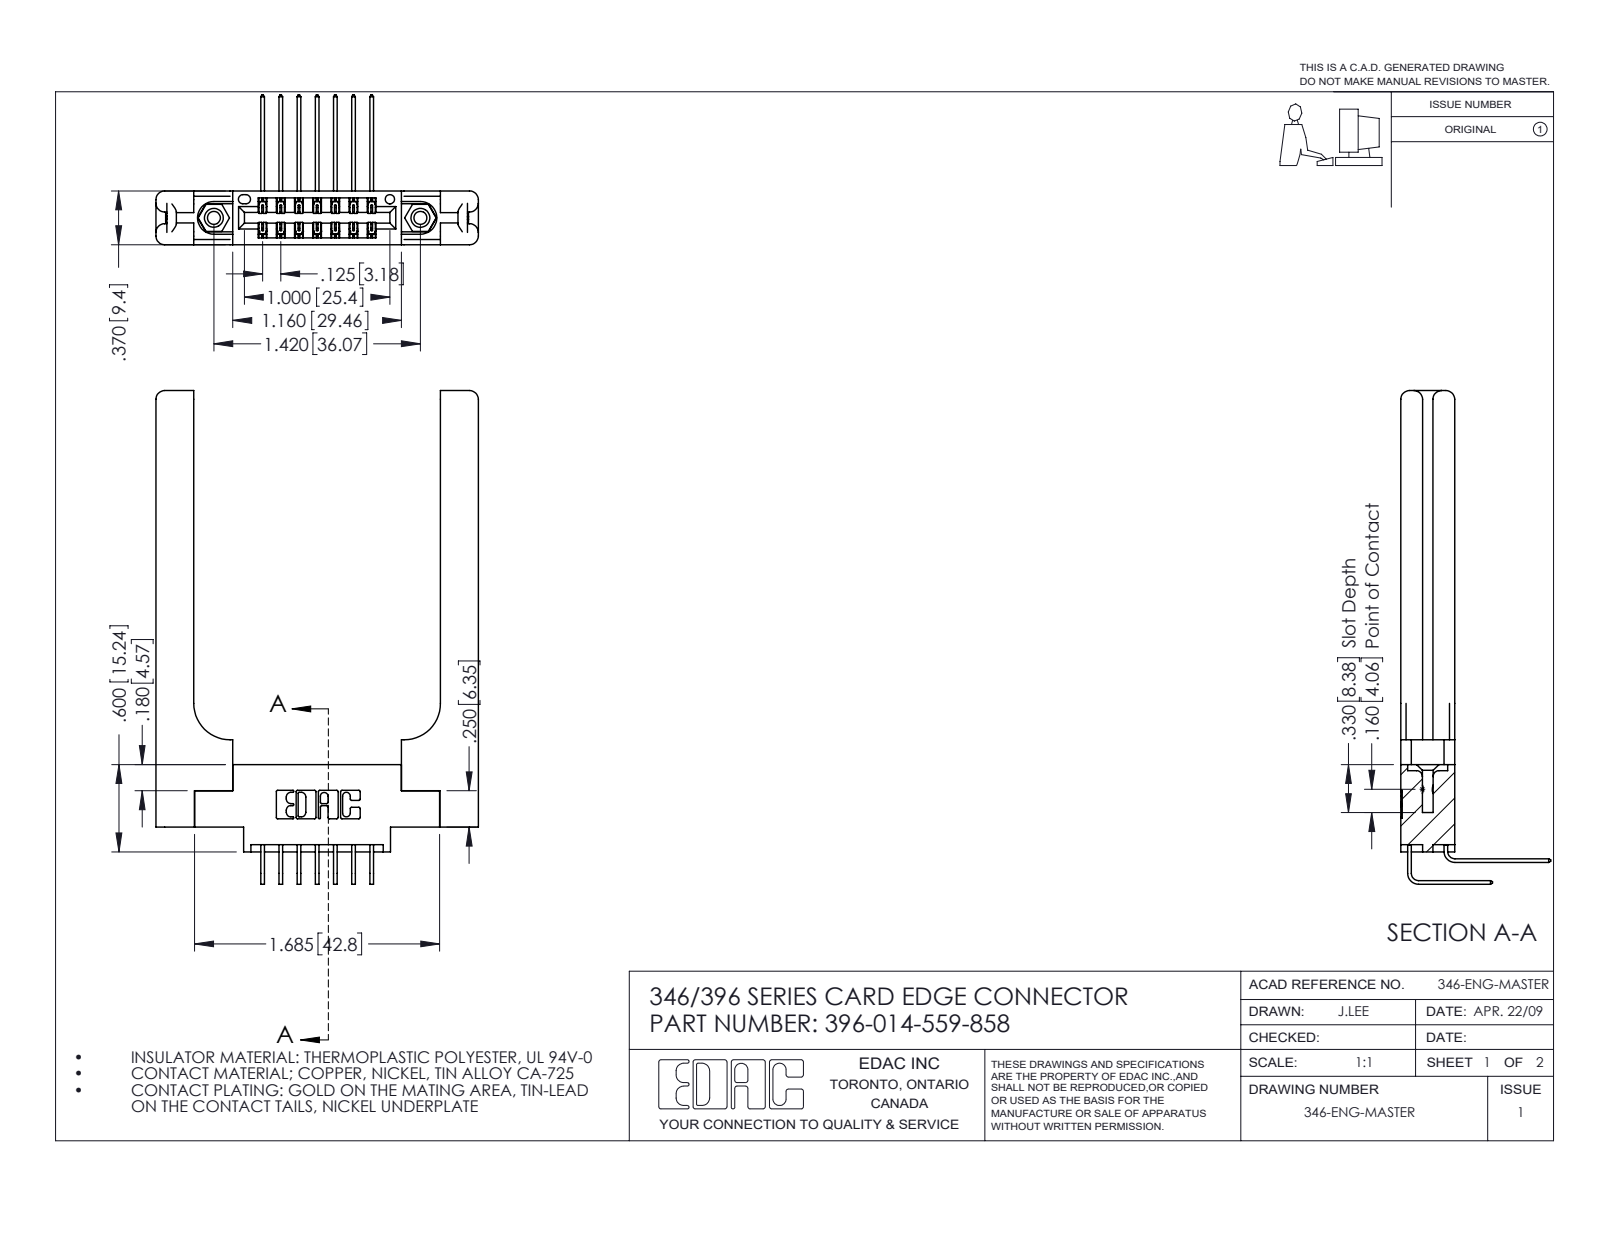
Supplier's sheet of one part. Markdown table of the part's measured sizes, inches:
| quantity | value |
| --- | --- |
| part name | 346 Part_0.170 Offset - 0.156 Dia-TH; 345-292-001_559 Tail - 2; 396-014-559-858; 345-292-001_558 559 Tail - 1 (+2 more) |
| STEP written by | SolidWorks 2016 (CONFIG_CONTROL_DESIGN) |
| units | inches |
| bodies | 19 solids, 1138 faces (746 planar, 332 cylindrical, 60 other) |
| overall size | 3.393 × 2.216 × 1.03 |
| volume | 0.771 in³ |
| surface area | 18.69 in² |
| round holes (diameter × count) | 0.089 × 2, 0.125 × 2, 0.156 × 2, 0.064 × 1 |
| round bosses / shafts (diameter × count) | 0.155 × 2 |
| partial cylindrical surfaces (radius × count) | 0.01 × 22, 0.006 × 21, 0.06 × 16, 0.007 × 6, 0.031 × 6, 0.026 × 3, 0.014 × 2, 0.022 × 2 |
| main face-to-face distances | 0.37, 0.15, 0.22, 0.072, 0.148, 0.048, 0.25, 0.025, 0.322, 0.102 |
| hole center spacings | 0.246, 1.217, 1.42 |
